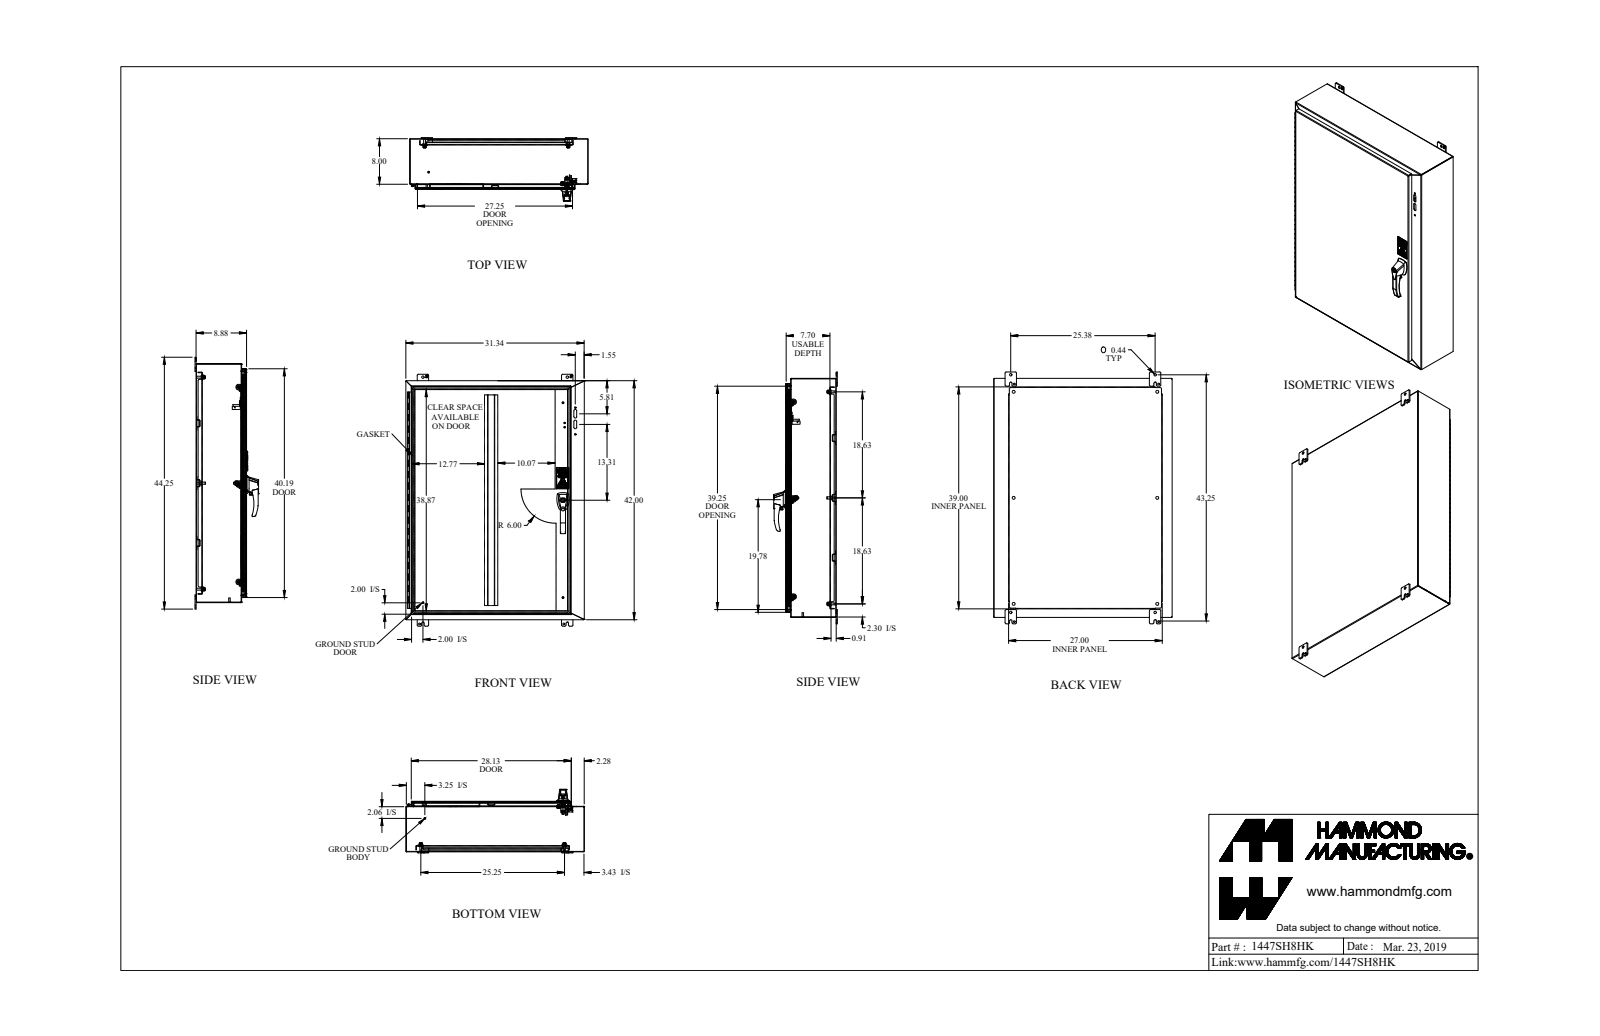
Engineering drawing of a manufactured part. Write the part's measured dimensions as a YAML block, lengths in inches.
part_name: "1447SH8HK"
step_written_by: "SolidWorks 2019 (AUTOMOTIVE_DESIGN)"
units: inches
bodies: {solids: 67, faces: 1555, planar: 963, cylindrical: 460, other: 132}
overall_size: [44.25, 31.375, 11.177]
volume: 465.9
surface_area: 11840
round_holes:
  - {diameter: 0.176, count: 6}
  - {diameter: 0.313, count: 6}
  - {diameter: 0.5, count: 6}
  - {diameter: 0.307, count: 4}
  - {diameter: 0.437, count: 4}
  - {diameter: 0.445, count: 4}
  - {diameter: 0.25, count: 3}
  - {diameter: 0.265, count: 3}
  - {diameter: 0.413, count: 3}
  - {diameter: 0.156, count: 2}
  - {diameter: 0.173, count: 2}
  - {diameter: 0.196, count: 2}
round_bosses_or_shafts:
  - {diameter: 0.375, count: 11}
  - {diameter: 0.25, count: 9}
  - {diameter: 1, count: 7}
  - {diameter: 0.65, count: 6}
  - {diameter: 0.33, count: 6}
  - {diameter: 0.156, count: 6}
  - {diameter: 0.63, count: 2}
  - {diameter: 0.51, count: 2}
partial_cylinders:
  - {radius: 0.187, count: 38}
  - {radius: 0.079, count: 28}
  - {radius: 0.25, count: 21}
  - {radius: 0.007, count: 16}
  - {radius: 0.115, count: 16}
  - {radius: 0.125, count: 16}
  - {radius: 0.03, count: 10}
  - {radius: 0.151, count: 8}
face_to_face_distances: [0.072, 8.803, 8.731, 8.875, 0.095, 7.771, 7.699, 1.032, 1.104, 7.866]
hole_center_spacings: [25.375, 31.376, 1.111, 25.25, 1.735, 1.736, 17.109, 17.11]
